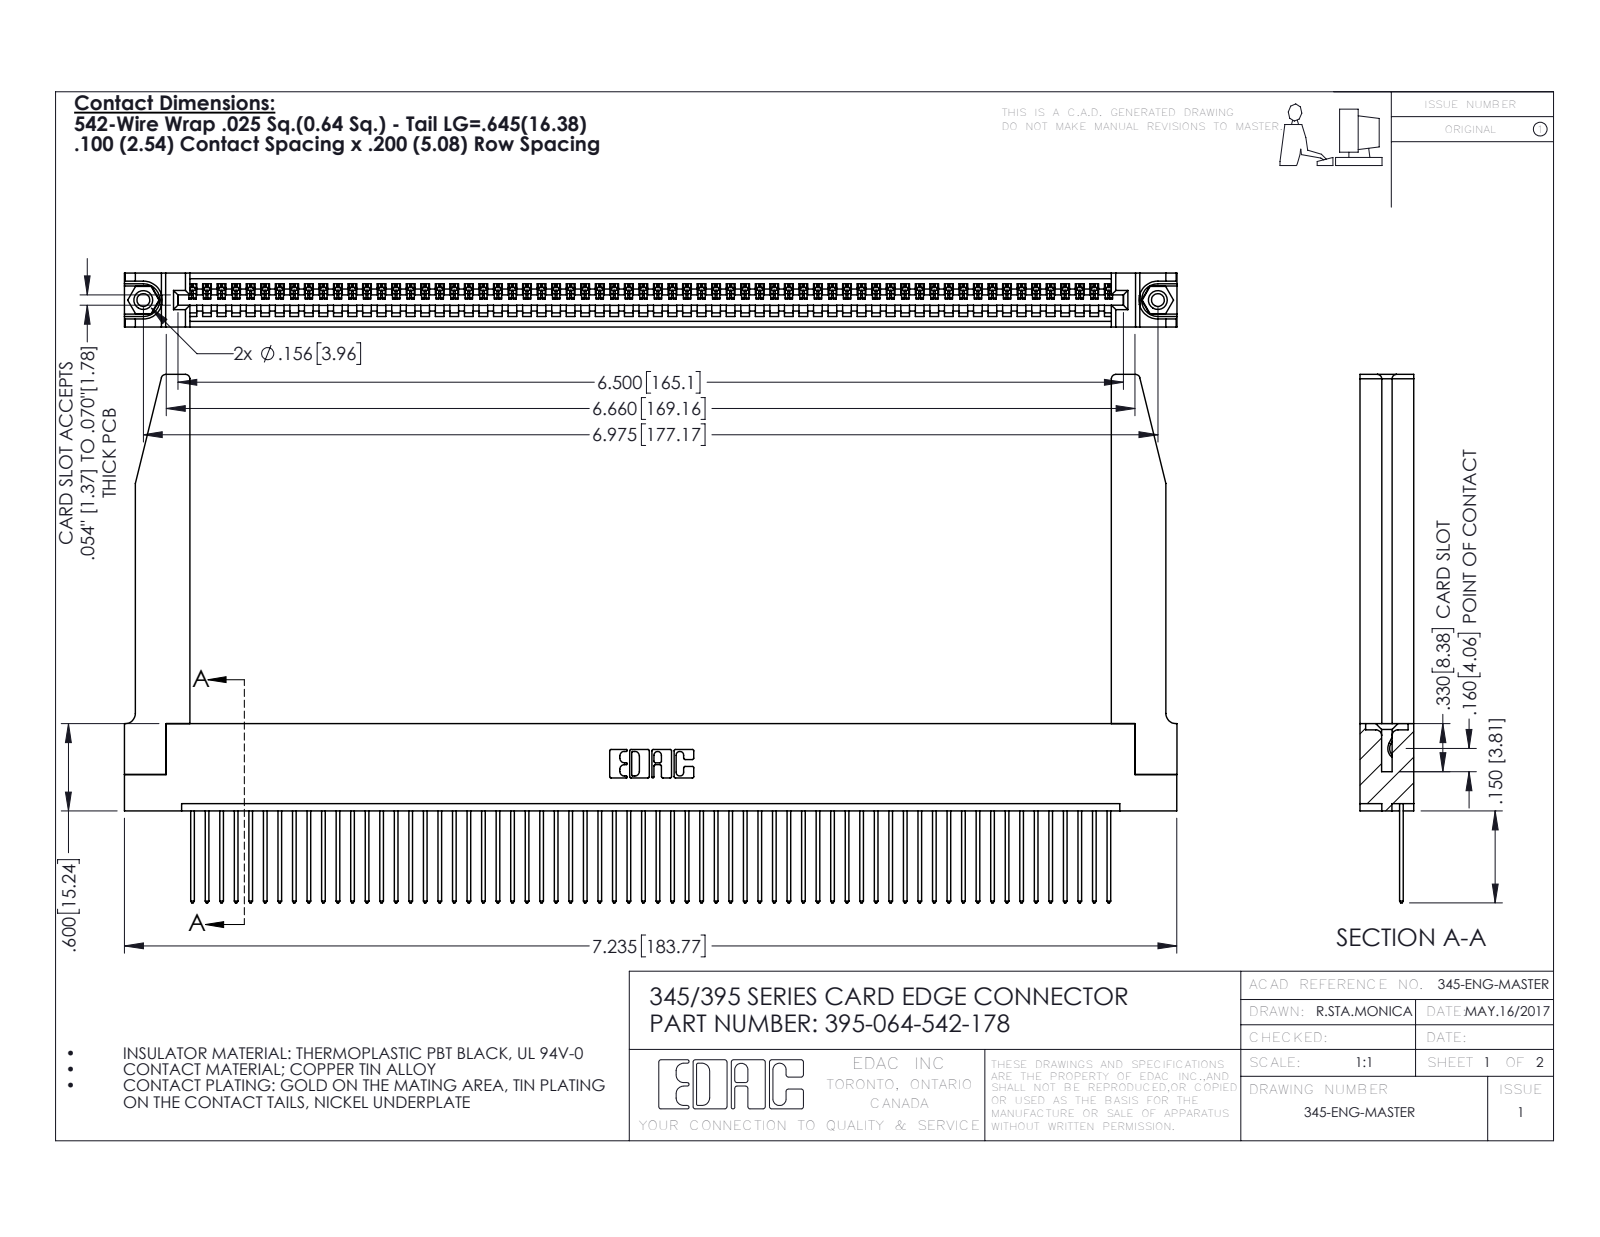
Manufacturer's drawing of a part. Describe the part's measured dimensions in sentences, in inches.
The part is named "345-250-001_345-250-001-102; 395-064-542-178; 345 Part_Flush Mounting Lugs - 0.156 Dia-TH; 345-220-078_345-220-078 (+1 more)". Its 3-D file was written by "SolidWorks 2016 (CONFIG_CONTROL_DESIGN)". It is 69 solids with 4072 faces: 2782 planar, 1238 cylindrical and 52 other. Overall it measures 7.236 by 3.632 by 0.37 inches. Its volume is 1.559 cubic inches and its surface area 49.09 square inches. Round holes: 2 of diameter 0.089, 2 of diameter 0.125, 2 of diameter 0.156, 1 of diameter 0.064. Round bosses or shafts: 2 of diameter 0.155. Partial cylindrical surfaces (rounded edges, fillets, slot ends): 128 of radius 0.006, 128 of radius 0.01, 22 of radius 0.01, 8 of radius 0.03, 6 of radius 0.007, 6 of radius 0.031, 3 of radius 0.026, 2 of radius 0.031. The main face-to-face distances are 0.072, 0.298, 0.37, 0.098, 0.272, 0.025, 0.2, 0.225, 0.148, 0.15. The hole center spacings are 0.27, 6.739, 6.975.
